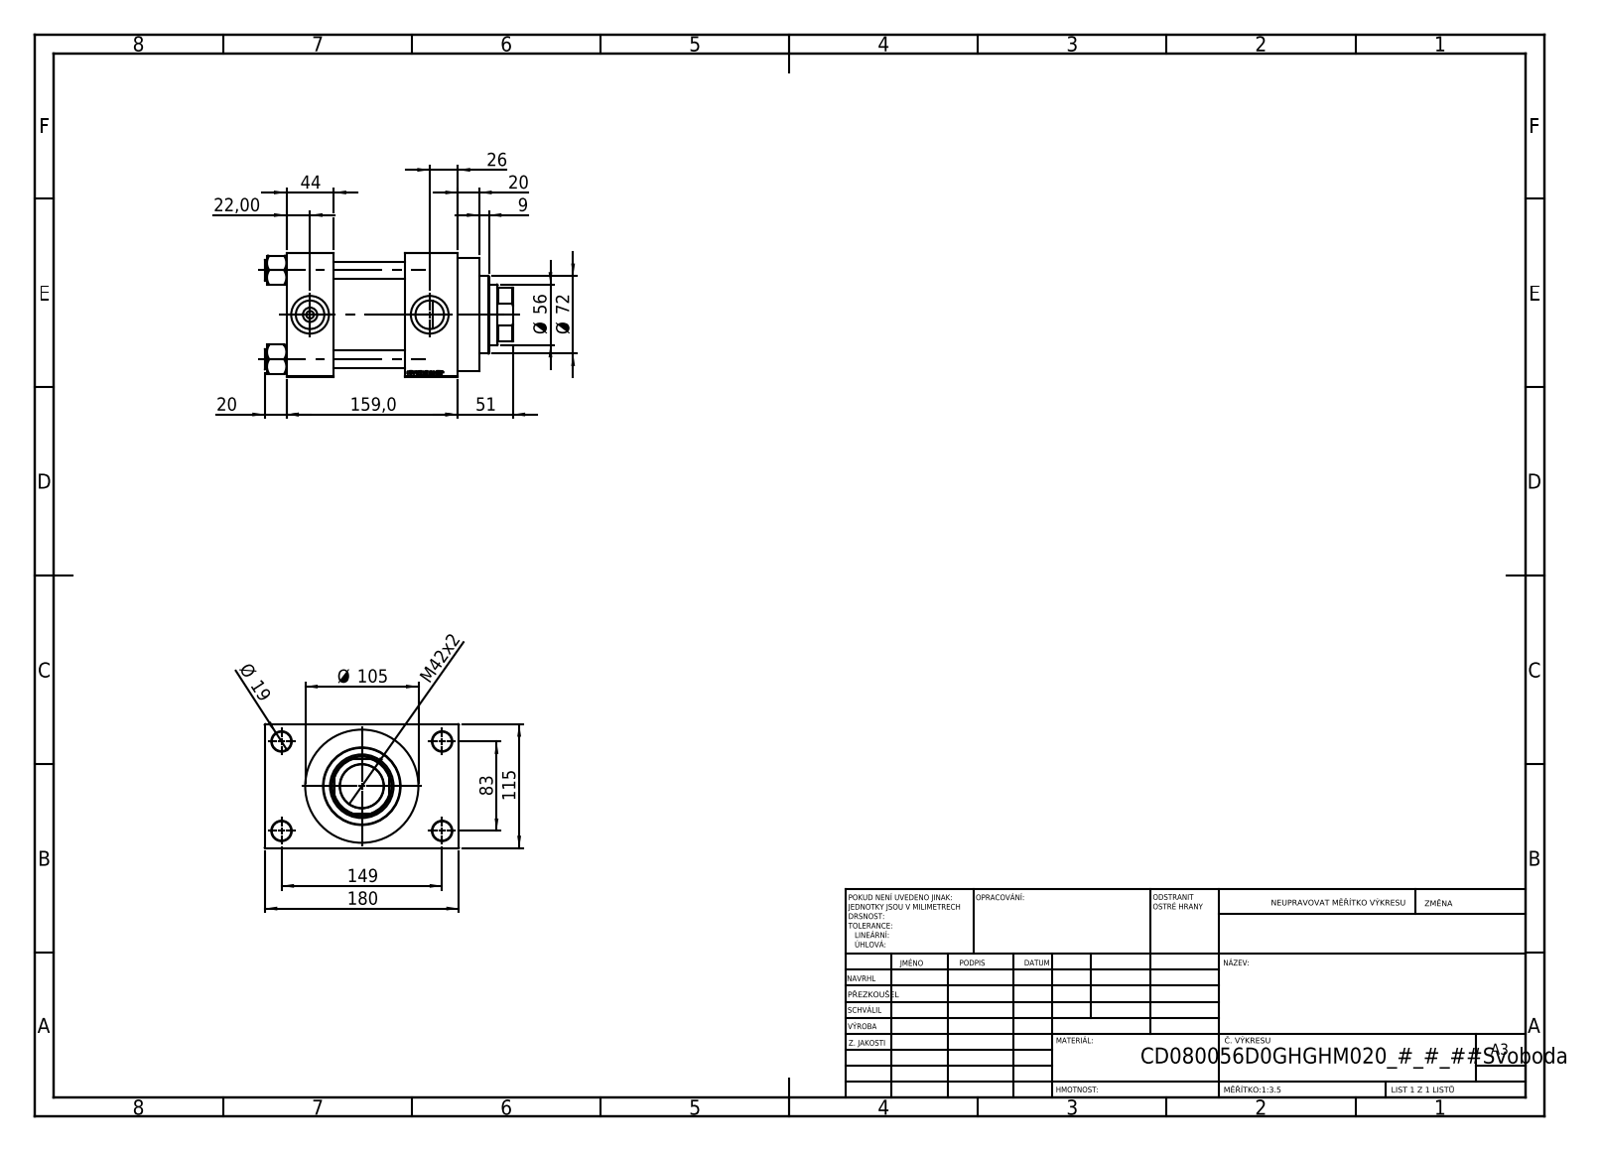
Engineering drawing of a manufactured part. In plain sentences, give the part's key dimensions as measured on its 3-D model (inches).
The part is named "V215CD_VC_A; V215CD_VCP_D; V215CD_NUT_M5_D; V215CD_D_TYCINKA (+1 more)". Its 3-D file was written by "SolidWorks 2019 (CONFIG_CONTROL_DESIGN)". It is 11 solids with 1148 faces: 544 planar, 86 cylindrical and 518 other. Overall it measures 9.055 by 7.087 by 4.528 inches. Its volume is 128.3 cubic inches and its surface area 481.6 square inches. Round holes: 4 of diameter 0.63, 4 of diameter 0.709, 2 of diameter 0.276, 2 of diameter 1.041, 2 of diameter 1.378, 1 of diameter 1.594, 1 of diameter 2.205, 1 of diameter 2.323, 1 of diameter 2.402, 1 of diameter 2.835, 1 of diameter 3.15. Round bosses or shafts: 4 of diameter 0.748, 1 of diameter 4.134, 1 of diameter 3.386. Partial cylindrical surfaces (rounded edges, fillets, slot ends): 1 of radius 1.063. The main face-to-face distances are 4.528, 2.598, 4.331, 1.732, 6.26, 1.929, 1.28, 5.807, 0.787, 2.717. The hole center spacings are 1.305, 2.302, 3.256, 3.357, 3.513, 4.561, 5.607, 3.268.
